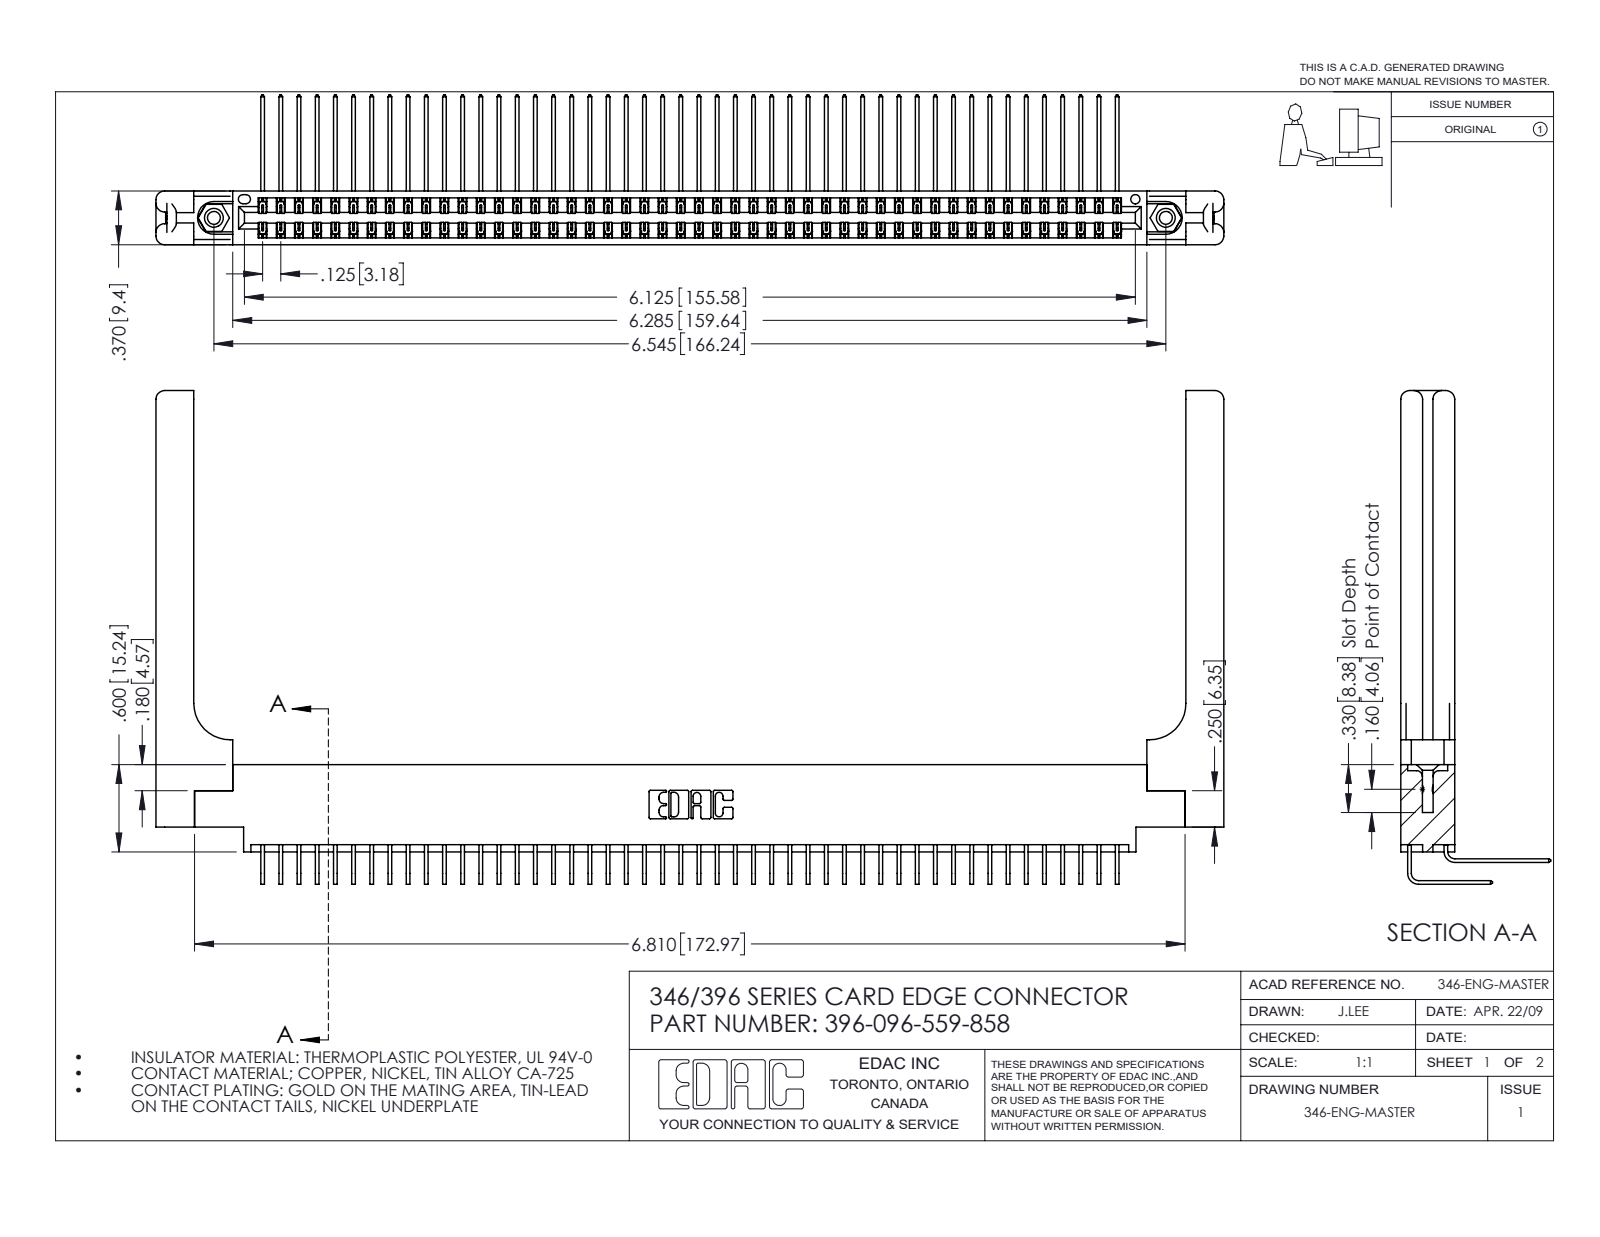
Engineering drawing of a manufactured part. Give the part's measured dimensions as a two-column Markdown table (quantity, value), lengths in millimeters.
| quantity | value |
| --- | --- |
| part name | 346 Part_0.170 Offset - 0.156 Dia-TH; 346-220-058_345-220-058; 396-096-559-858; 345-292-001_558 559 Tail - 1 (+2 more) |
| STEP written by | SolidWorks 2016 (CONFIG_CONTROL_DESIGN) |
| units | millimeters |
| bodies | 101 solids, 5566 faces (3780 planar, 1726 cylindrical, 60 other) |
| overall size | 186.5 × 86.2 × 26.2 |
| volume | 26 120 mm³ |
| surface area | 33 510 mm² |
| round holes (diameter × count) | 2.3 × 2, 3.2 × 2, 4 × 2, 1.6 × 1 |
| round bosses / shafts (diameter × count) | 3.9 × 2 |
| partial cylindrical surfaces (radius × count) | 0.2 × 144, 0.3 × 22, 1.5 × 16, 0.2 × 6, 0.8 × 6, 0.7 × 3, 0.4 × 2, 0.6 × 2 |
| main face-to-face distances | 1.2, 9.4, 8.2, 1.8, 0.6, 3.8, 3.8, 6.4, 7.6, 7 |
| hole center spacings | 6.2, 160.9, 166.2 |
